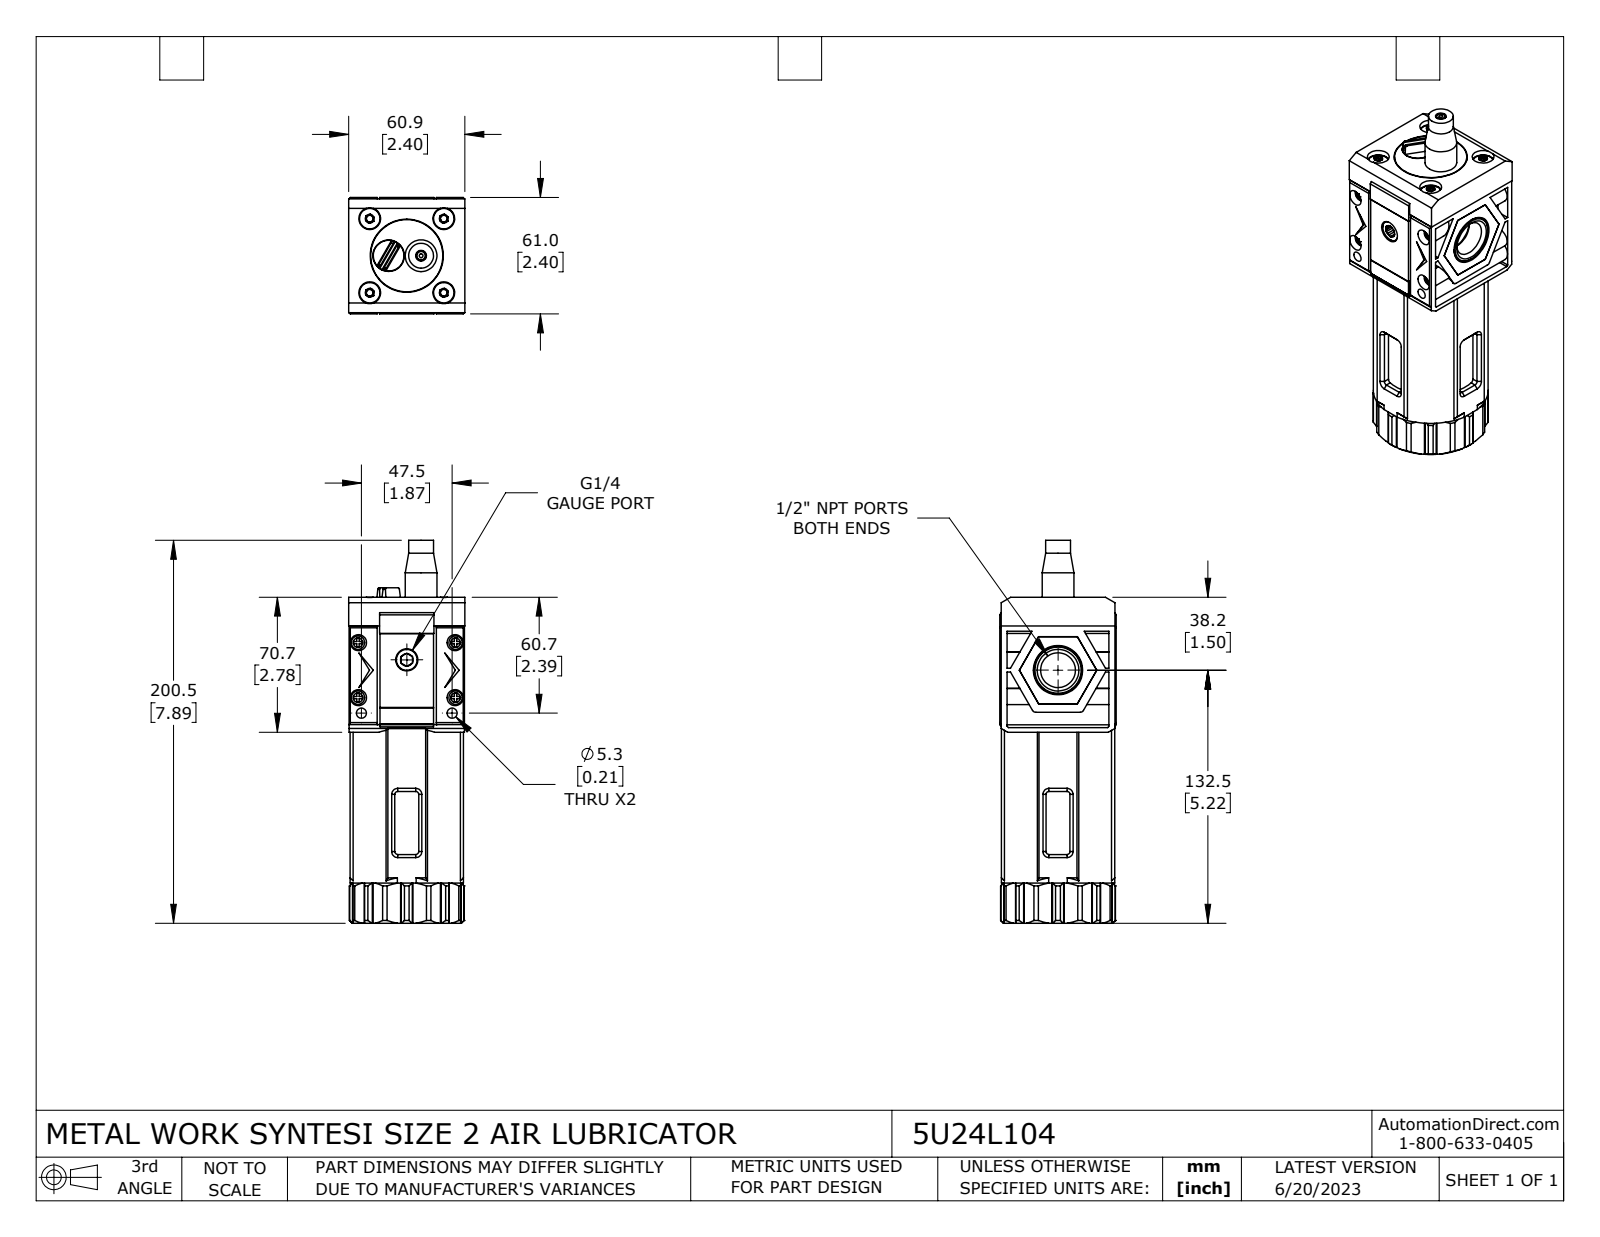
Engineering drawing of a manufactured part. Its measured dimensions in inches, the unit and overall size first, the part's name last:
Units: inches
Overall size (bounding box): 7.894 × 2.402 × 2.398
Round holes (diameter × count): ⌀0.128 ×4, ⌀0.165 ×4, ⌀0.331 ×4, ⌀0.449 ×4, ⌀0.209 ×2, ⌀0.22 ×1, ⌀0.457 ×1, ⌀0.65 ×1, ⌀1.25 ×1, ⌀1.508 ×1, ⌀1.929 ×1, ⌀1.969 ×1
Round bosses / shafts (diameter × count): ⌀0.276 ×4, ⌀0.189 ×4, ⌀0.15 ×4, ⌀1.488 ×1, ⌀1.248 ×1, ⌀1.035 ×1, ⌀0.925 ×1, ⌀0.917 ×1
Partial cylindrical surfaces — rounded edges, fillets, slot ends (radius × count): R0.011 ×28, R0.02 ×16, R0.059 ×8, R0.069 ×4, R0.191 ×4, R0.008 ×2, R0.079 ×2, R0.242 ×2
Main face-to-face distances: 2.39, 2.098, 5.303, 3.205, 1.13, 2.193, 2.402, 0.031, 3.11, 0.094
Hole centre spacings: 1.08, 1.528, 0.325, 0.857, 0.896, 1.057, 1.134, 1.265
Volume: 23.37 in³ · Surface area: 189.6 in²
Bodies: 14 solids, 1060 faces (531 planar, 318 cylindrical, 211 other)
Part name (STEP PRODUCT): 5U24L104
STEP written by: SolidWorks 2021 (CONFIG_CONTROL_DESIGN)
